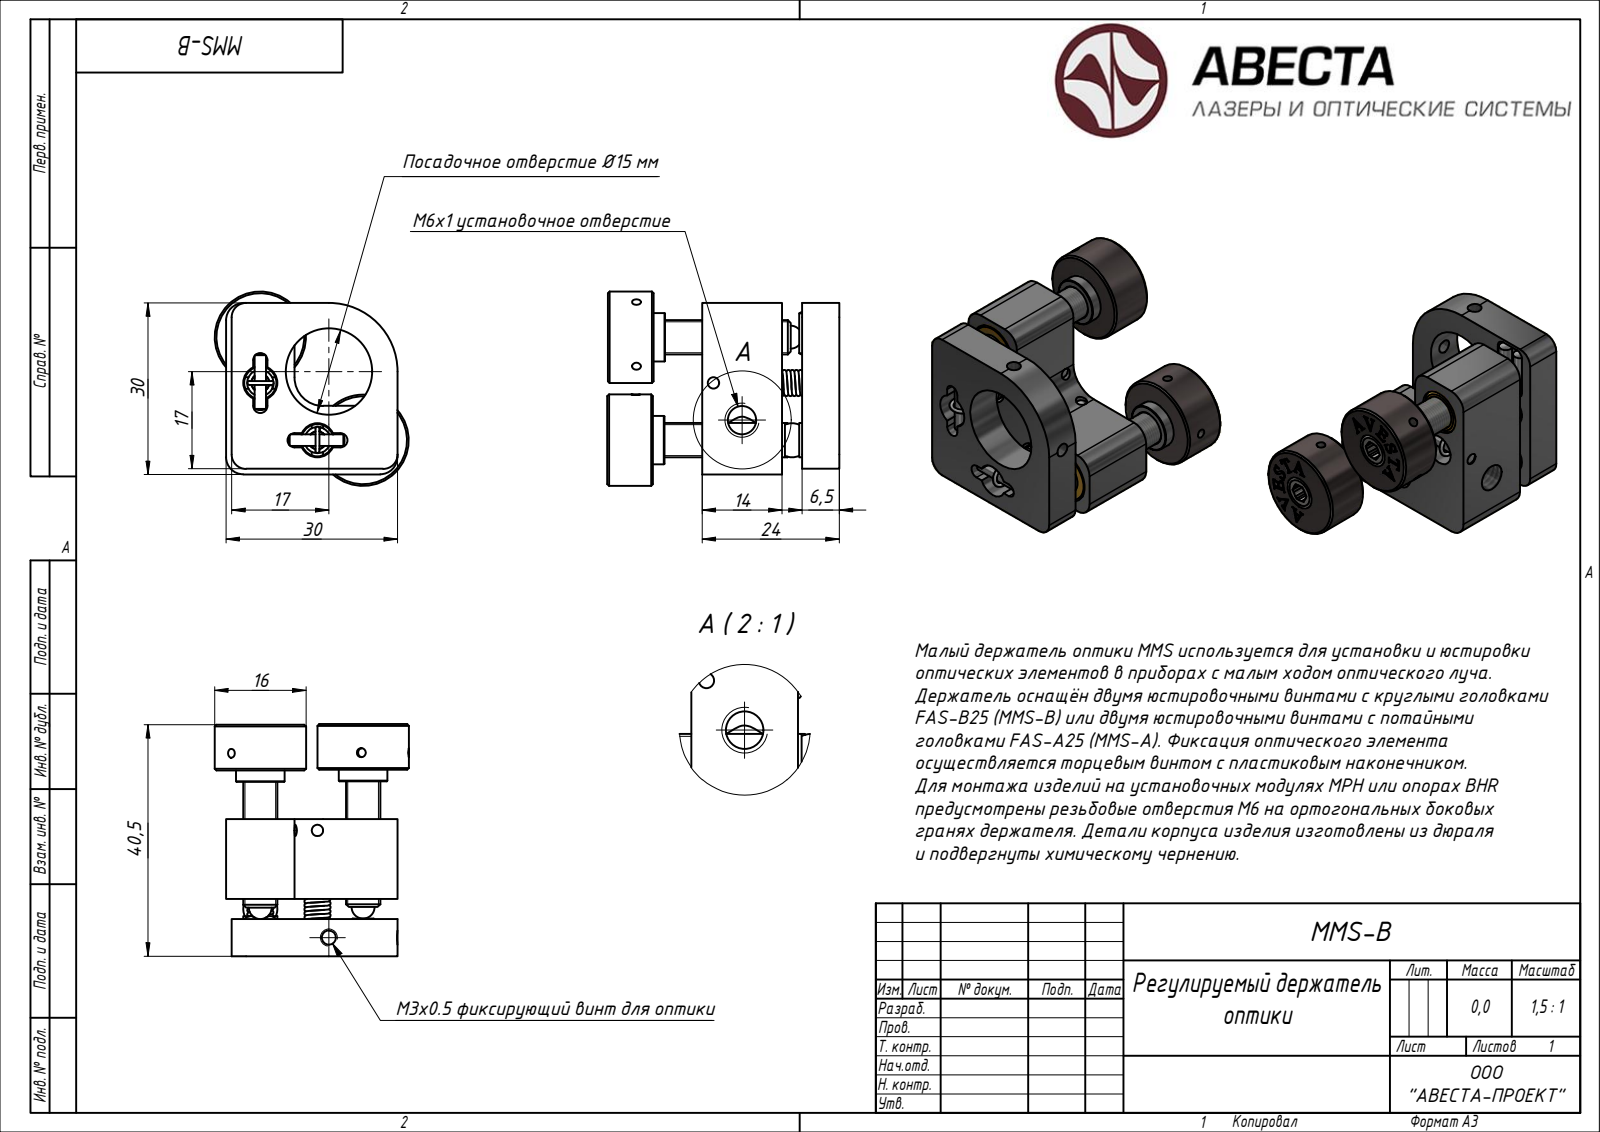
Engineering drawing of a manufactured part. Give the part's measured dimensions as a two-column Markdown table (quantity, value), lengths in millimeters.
| quantity | value |
| --- | --- |
| STEP written by | ST-DEVELOPER v15 (AUTOMOTIVE_DESIGN) |
| units | millimeters |
| bodies | 35 solids, 857 faces (0 planar, 0 cylindrical, 857 other) |
| overall size | 40.6 × 34 × 34 |
| volume | 14 574 mm³ |
| surface area | 14 762 mm² |
